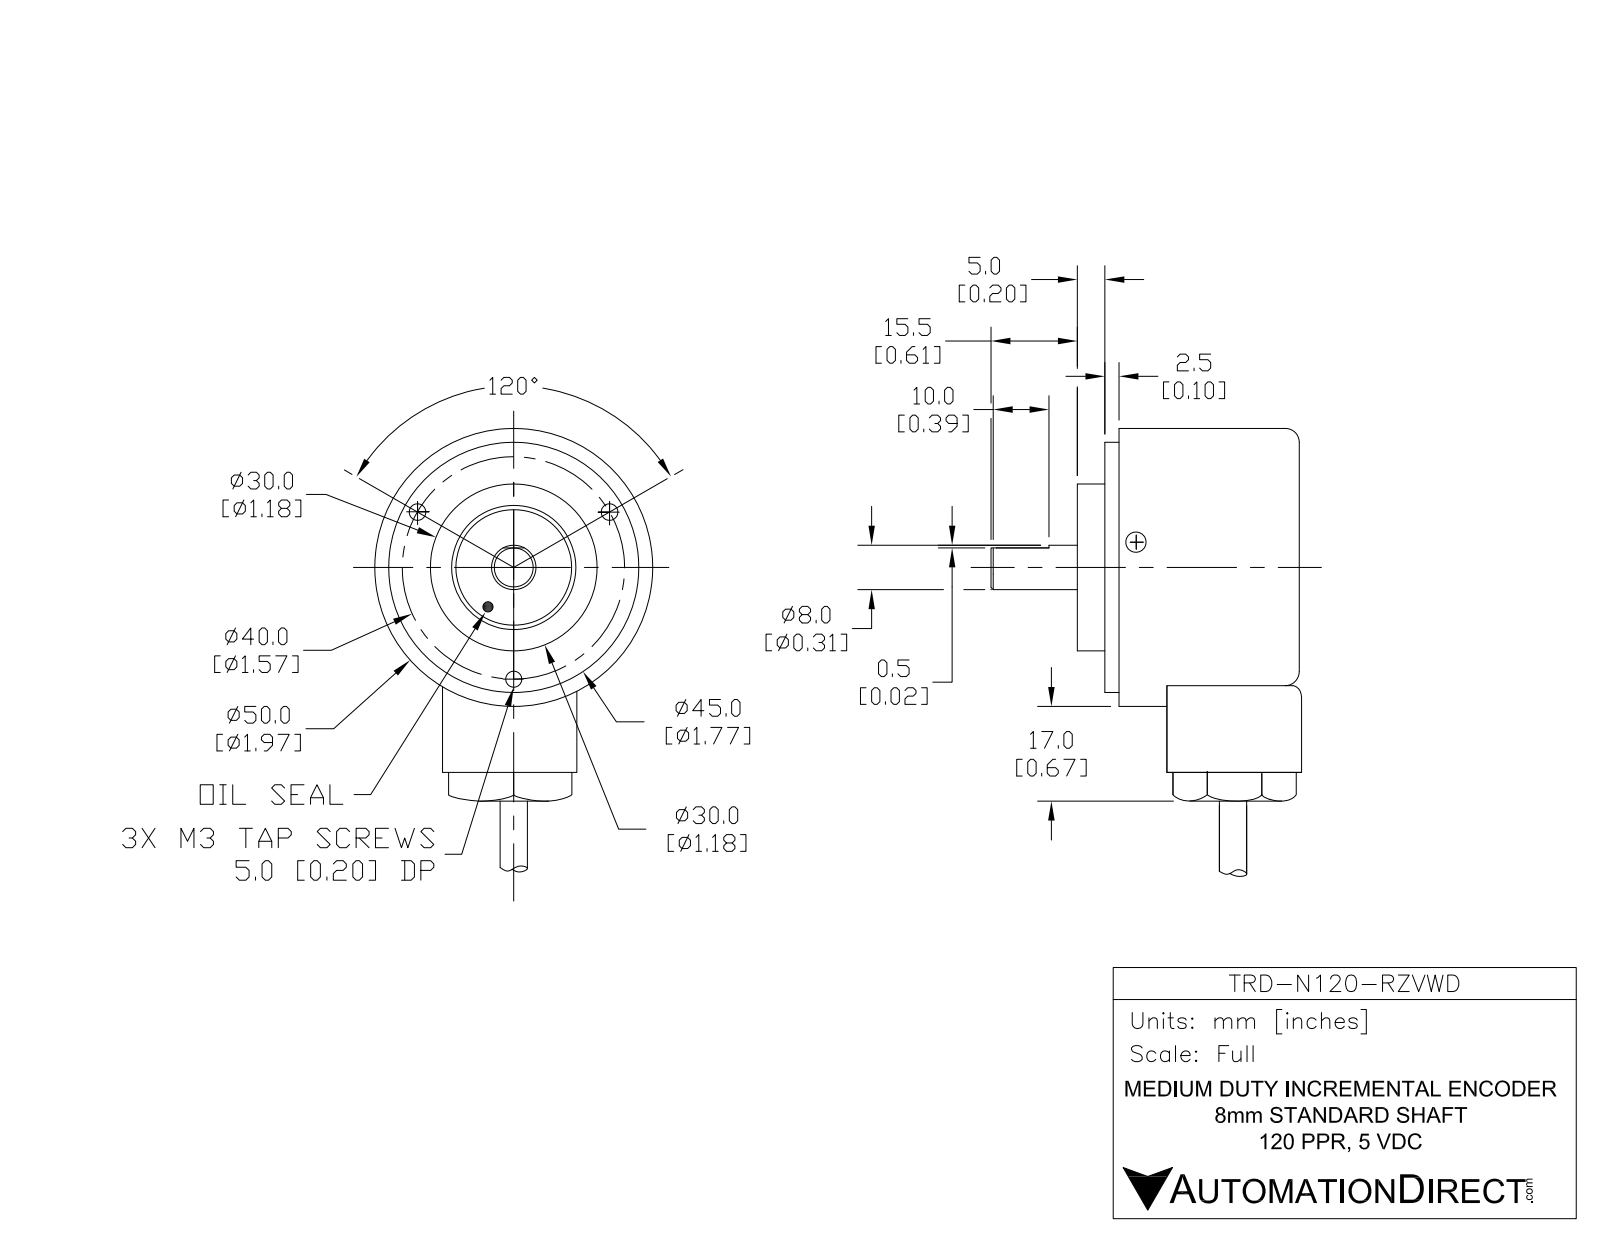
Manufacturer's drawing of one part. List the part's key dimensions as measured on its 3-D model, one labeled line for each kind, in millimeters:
Part name (STEP PRODUCT): TRD-N-RZ
STEP written by: SolidWorks 2016 (AUTOMOTIVE_DESIGN)
Units: millimetres
Bodies: 1 solid, 95 faces (25 planar, 23 cylindrical, 47 other)
Overall size (bounding box): 118.2 × 58.5 × 51.32
Volume: 76 429 mm³ · Surface area: 12 939 mm²
Round holes (diameter × count): ⌀2.5 ×3, ⌀22 ×1
Round bosses / shafts (diameter × count): ⌀6 ×2, ⌀45 ×1, ⌀30 ×1, ⌀11 ×1, ⌀8 ×1
Partial cylindrical surfaces — rounded edges, fillets, slot ends (radius × count): R4 ×3
Main face-to-face distances: 36.5, 2.5, 34, 1, 3.5, 37.5, 5, 4, 7.5, 41.5
Hole centre spacings: 20, 34.64
